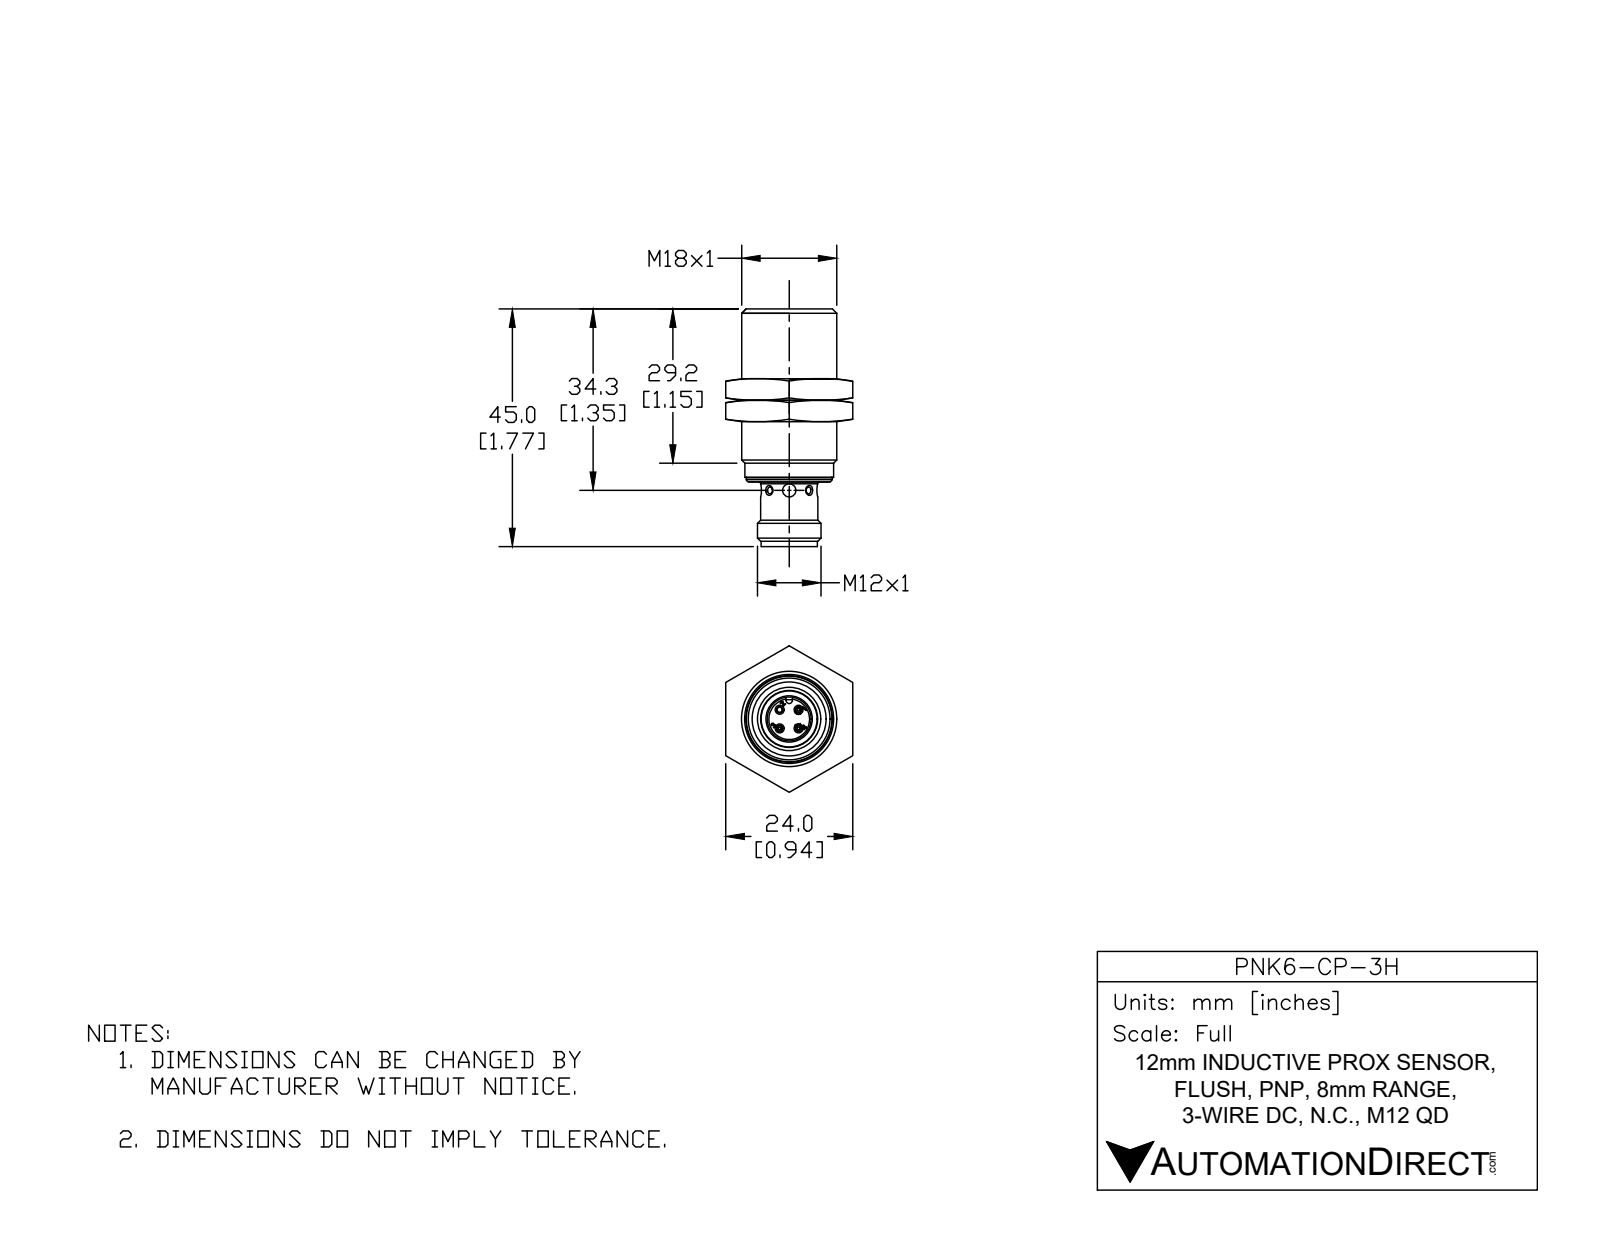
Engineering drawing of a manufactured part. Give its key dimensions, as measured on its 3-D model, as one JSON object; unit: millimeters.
{"part_name": "PNK6-CP-3H", "step_written_by": "SolidWorks 2017 (AUTOMOTIVE_DESIGN)", "units": "millimeters", "bodies": {"solids": 1, "faces": 476, "planar": 118, "cylindrical": 129, "other": 229}, "overall_size": [45, 18, 18], "volume_mm3": 6570, "surface_area_mm2": 4930, "round_holes": [[1, 3], [1.1, 3], [2.5, 2], [1, 1], [8.2, 1], [8.3, 1], [10, 1], [15.7, 1]], "round_bosses_or_shafts": [[1, 9], [18, 1], [16.8, 1], [16.3, 1], [16.2, 1], [15.6, 1], [12, 1], [10.8, 1]], "partial_cylinders_radius": [[0.1, 24], [1, 6], [1.8, 6], [0.6, 1], [0.8, 1]], "face_to_face_distances": [11.5, 0.8, 10.7, 31.4, 30.7, 19.9, 32.8, 1.4, 32.1, 21.3], "hole_center_spacings": [2.5, 3.5, 5]}
